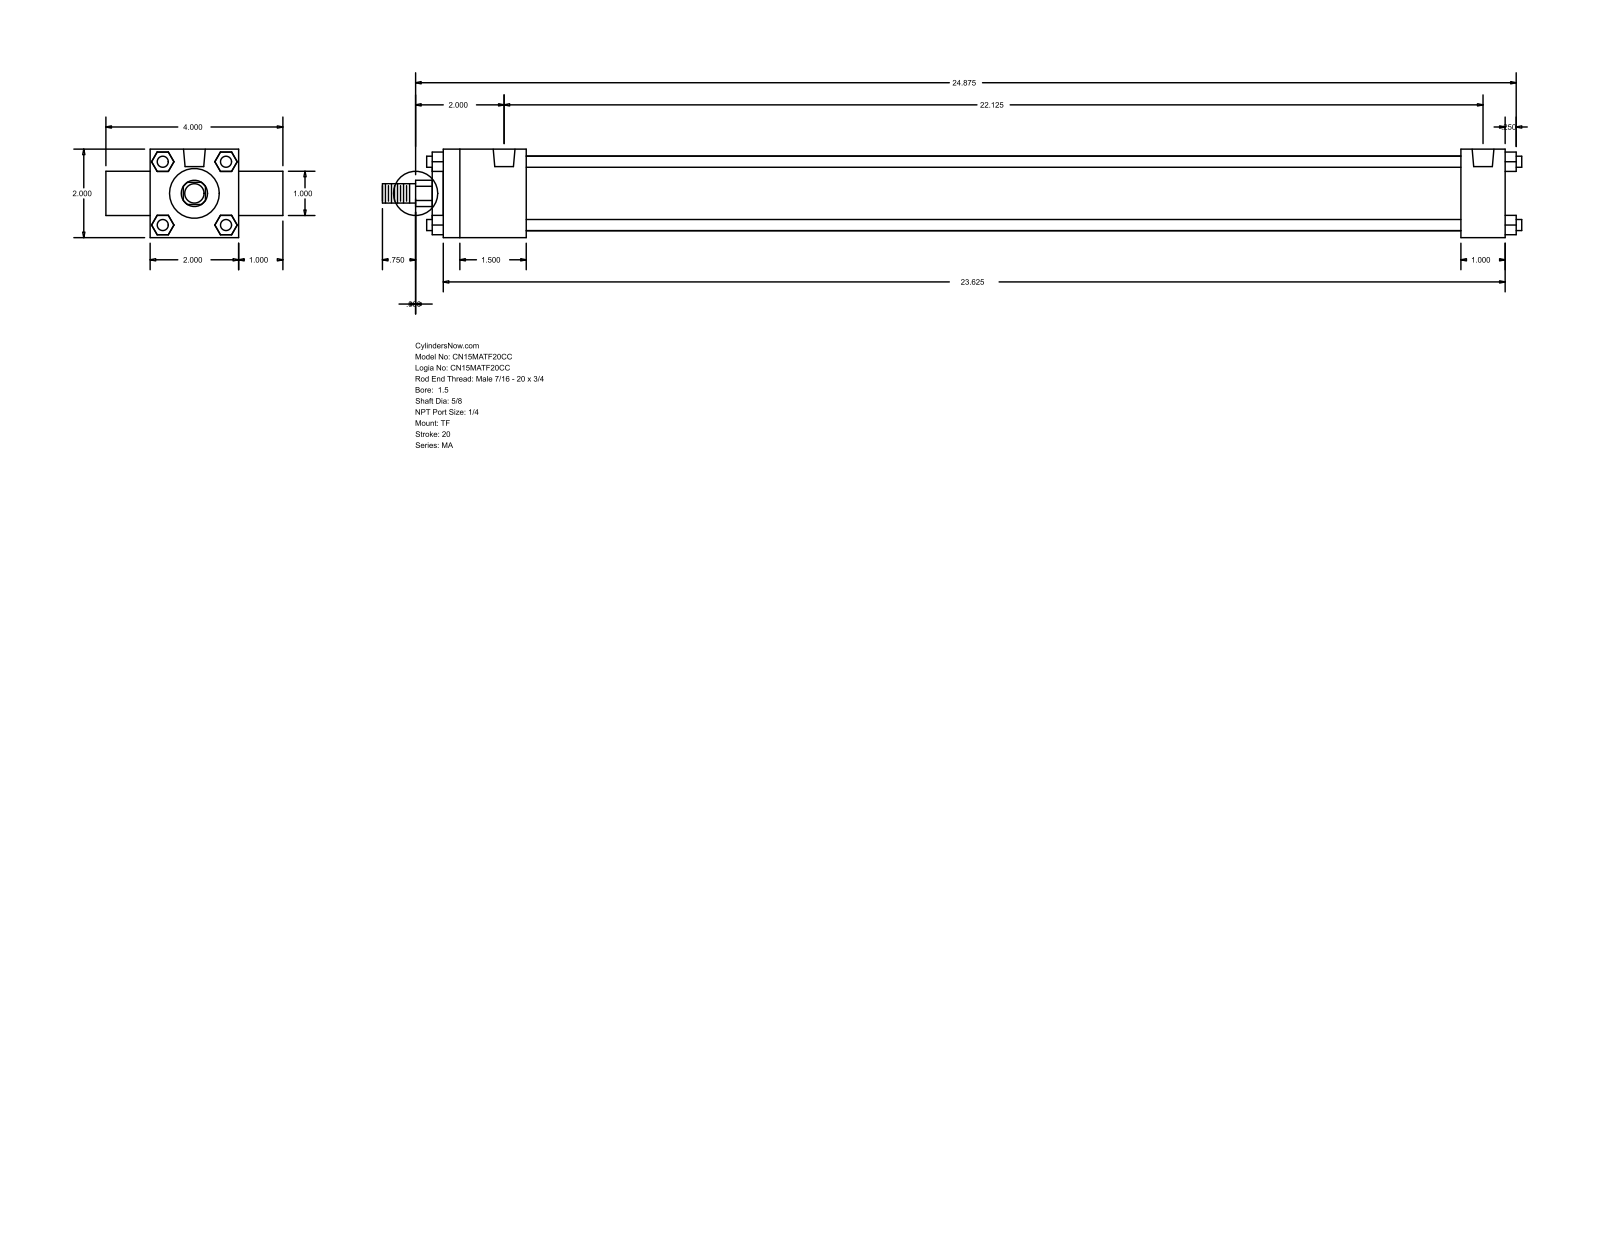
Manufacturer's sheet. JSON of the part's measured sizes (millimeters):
{"part_name": "MA_TF__0150_0.625", "step_written_by": "GSSL Pune (CONFIG_CONTROL_DESIGN)", "units": "millimeters", "bodies": {"solids": 0, "faces": 120, "planar": 92, "cylindrical": 28, "other": 0}, "overall_size": [654.05, 101.6, 50.8], "round_holes": [[7.94, 3], [12.49, 2]], "round_bosses_or_shafts": [[6.35, 4], [42.93, 1], [28.57, 1], [25.4, 1], [15.88, 1], [11.11, 1]], "partial_cylinders_radius": [[7.54, 1]], "face_to_face_distances": [50.8, 25.4, 609.6, 6.35, 615.95, 76.2, 47.62, 584.2, 536.58, 561.98], "hole_center_spacings": [561.97]}
